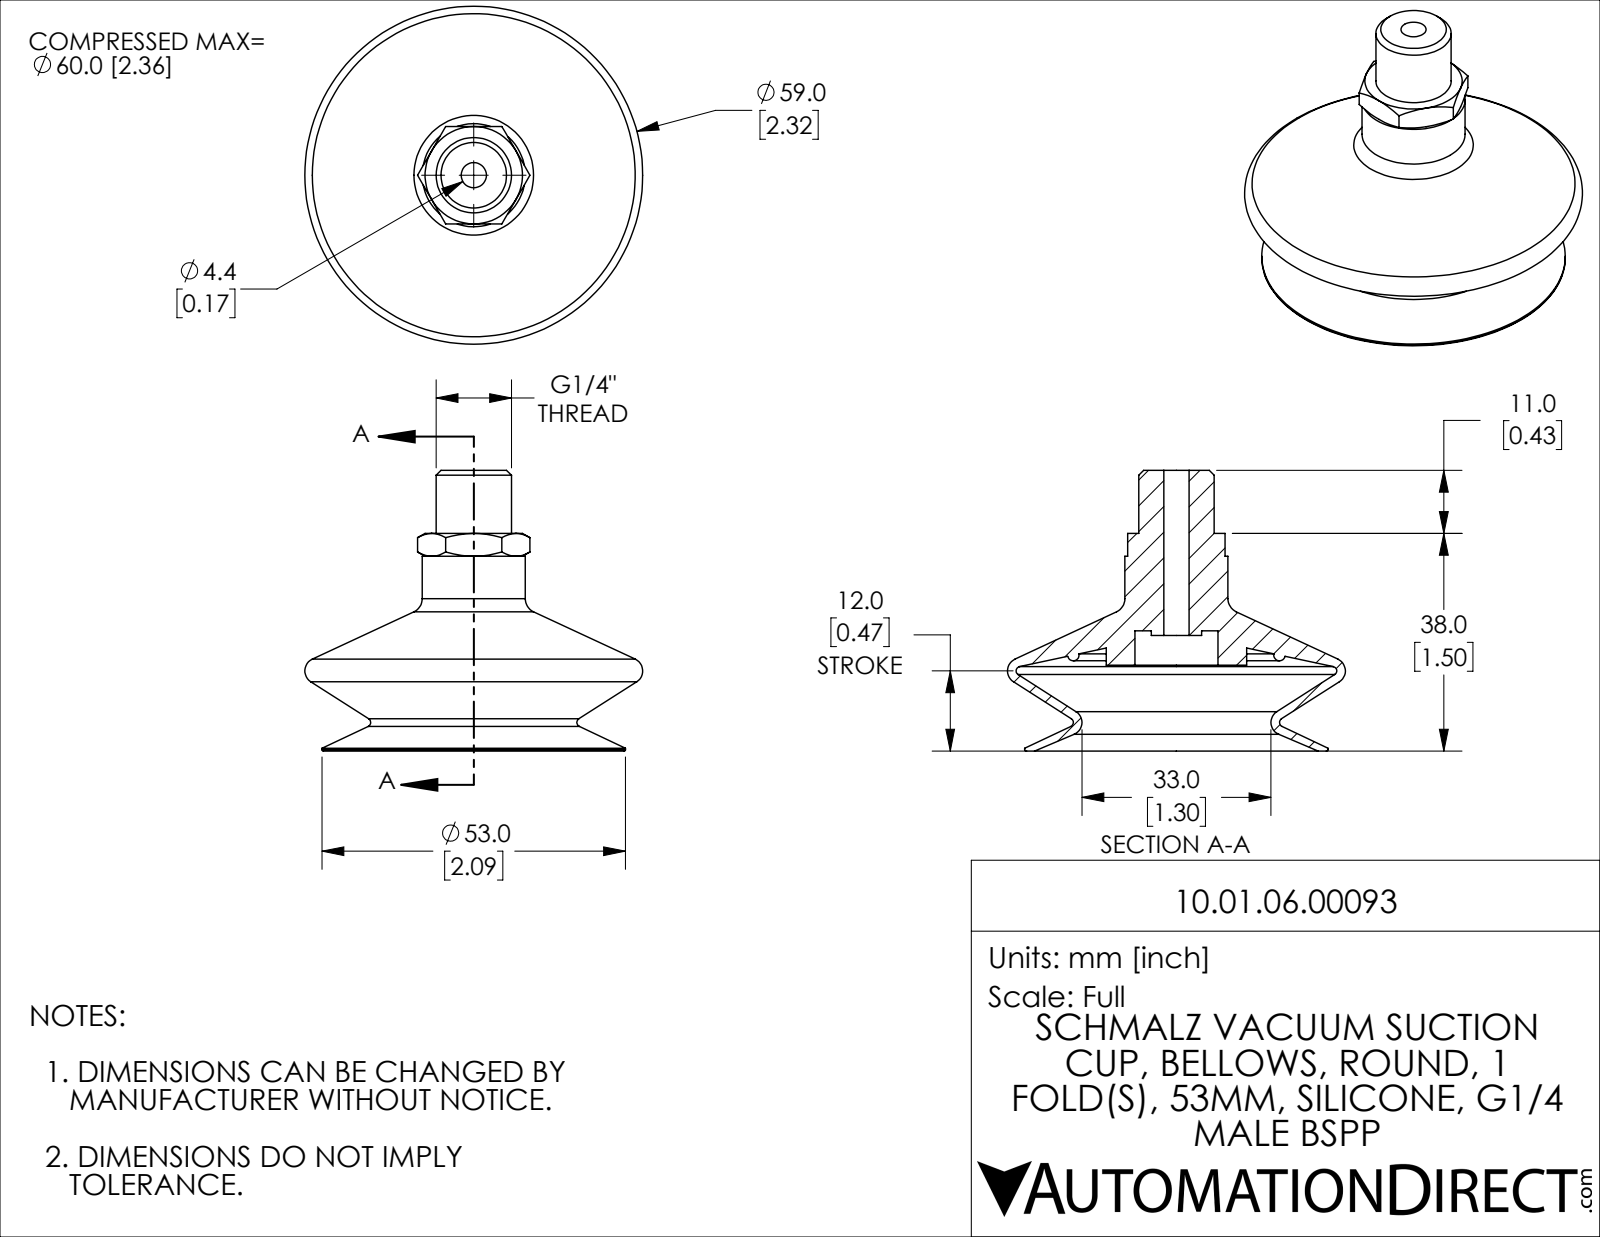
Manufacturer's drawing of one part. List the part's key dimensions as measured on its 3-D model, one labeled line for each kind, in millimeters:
Part name (STEP PRODUCT): 10.01.06.00093
STEP written by: SolidWorks 2021 (CONFIG_CONTROL_DESIGN)
Units: millimetres
Bodies: 1 solid, 79 faces (13 planar, 12 cylindrical, 54 other)
Overall size (bounding box): 59 × 59 × 49
Volume: 20 128 mm³ · Surface area: 15 306 mm²
Round holes (diameter × count): ⌀4.4 ×1, ⌀14.5 ×1
Round bosses / shafts (diameter × count): ⌀53 ×1, ⌀24.5 ×1, ⌀13.16 ×1, ⌀8.8 ×1
Main face-to-face distances: 15, 17, 34, 21, 6, 38, 23, 49, 28, 11
